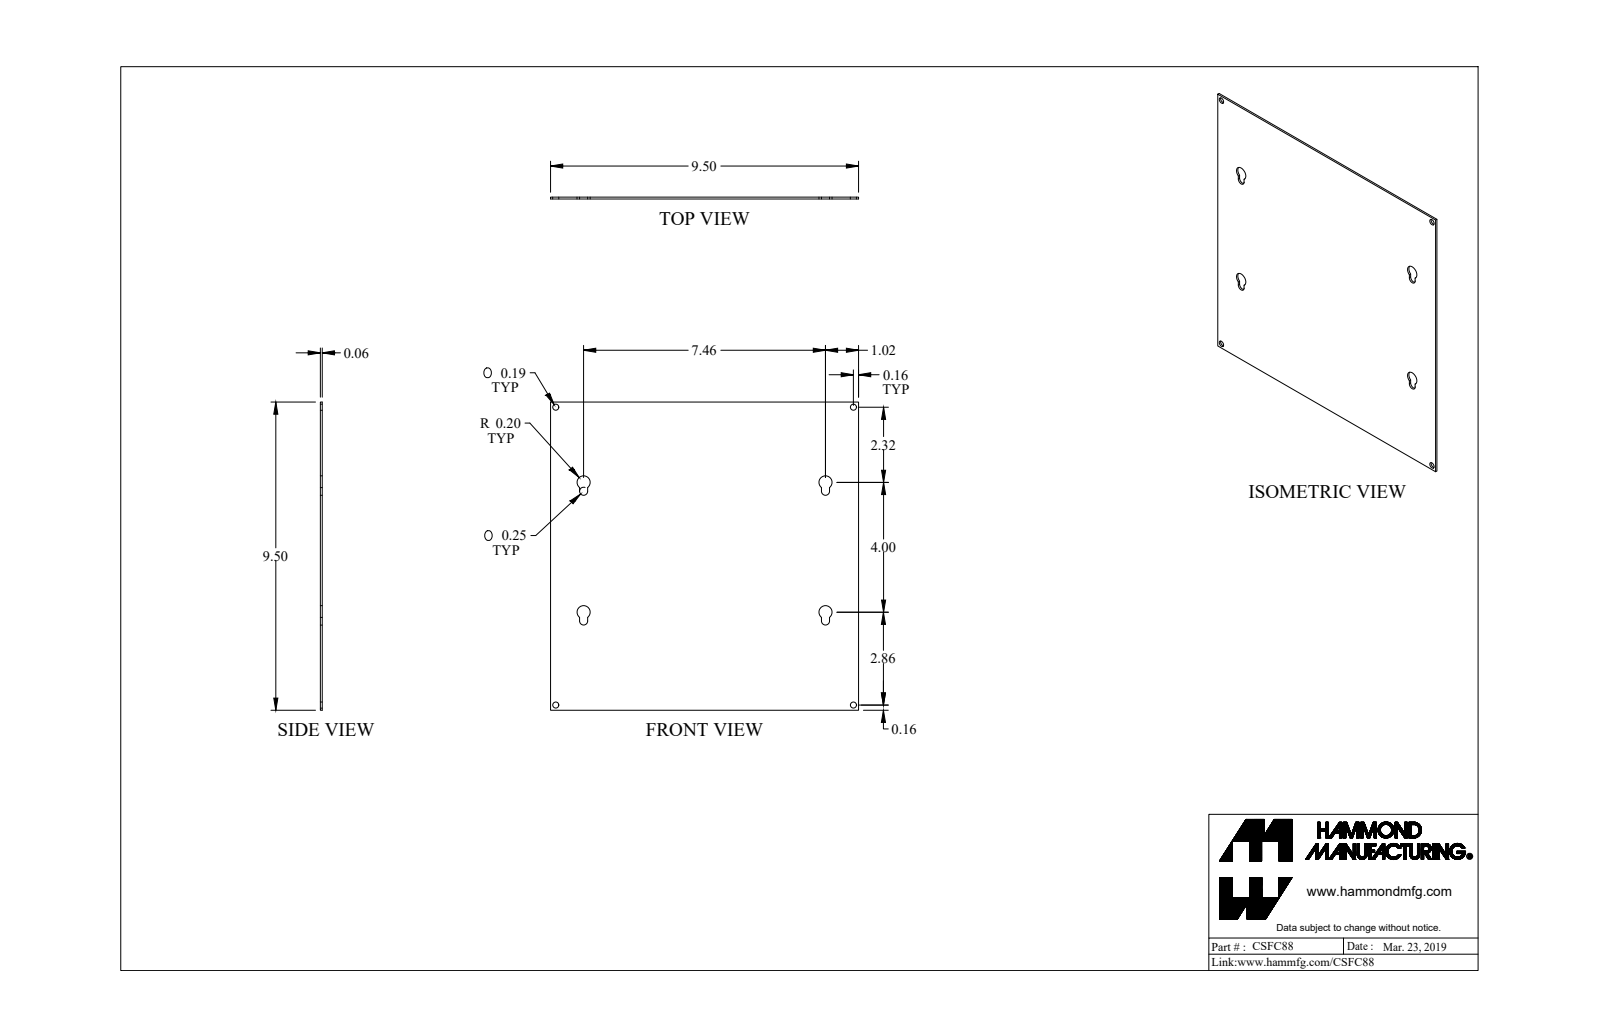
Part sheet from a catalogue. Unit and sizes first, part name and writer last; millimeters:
Units: millimetres
Overall size (bounding box): 241.3 × 241.3 × 1.4
Round holes (diameter × count): ⌀4.8 ×4
Partial cylindrical surfaces — rounded edges, fillets, slot ends (radius × count): R3.2 ×4, R5.2 ×4
Main face-to-face distances: 1.4, 241.3, 29.1, 212.2, 22.7, 218.6, 6.4, 189.5, 195.8, 183.1
Hole centre spacings: 233.2, 329.8
Volume: 83 540 mm³ · Surface area: 117 200 mm²
Bodies: 1 solid, 38 faces (14 planar, 24 cylindrical, 0 other)
Part name (STEP PRODUCT): CSFC88_Default
STEP written by: SolidWorks 2019 (CONFIG_CONTROL_DESIGN)
